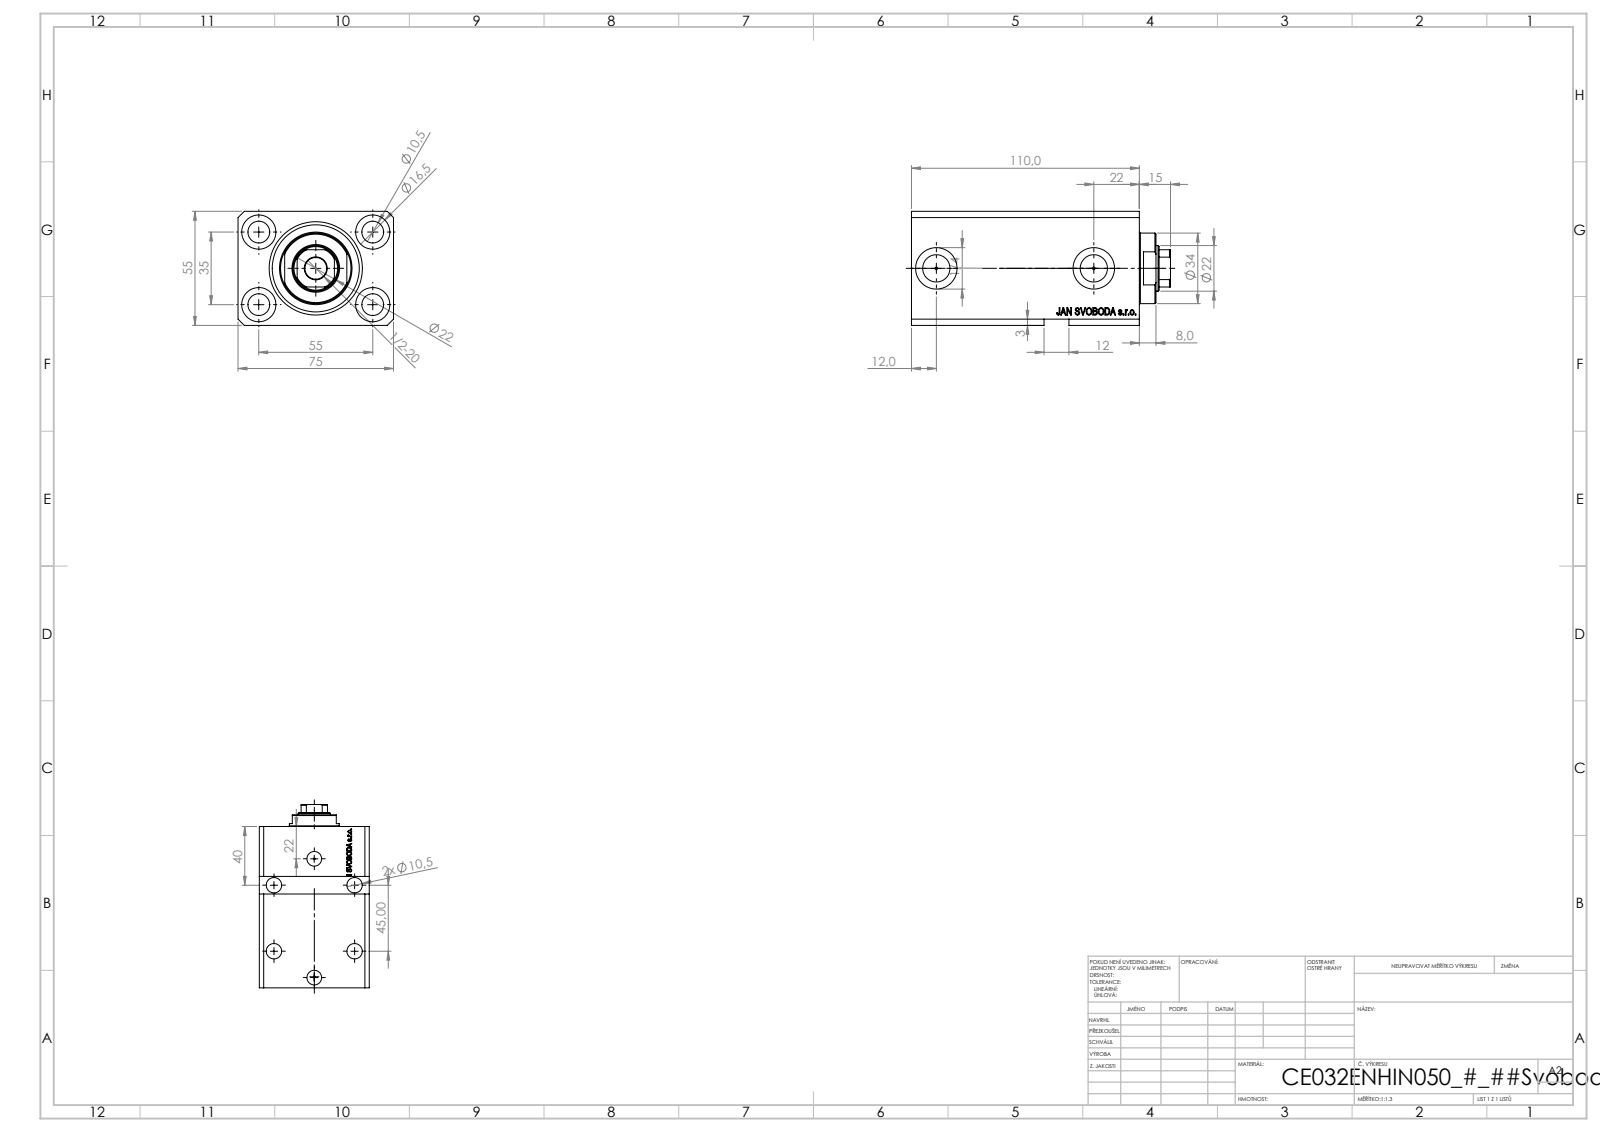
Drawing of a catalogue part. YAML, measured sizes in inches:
part_name: "V250CE_VC_E; V250CE_C_VCP; V250CE_E_Body"
step_written_by: "SolidWorks 2019 (CONFIG_CONTROL_DESIGN)"
units: inches
bodies: {solids: 3, faces: 914, planar: 438, cylindrical: 104, other: 372}
overall_size: [4.921, 2.953, 2.165]
volume: 22.52
surface_area: 132.4
round_holes:
  - {diameter: 0.413, count: 9}
  - {diameter: 0.049, count: 4}
  - {diameter: 0.65, count: 4}
  - {diameter: 0.394, count: 2}
  - {diameter: 0.518, count: 2}
  - {diameter: 0.787, count: 2}
  - {diameter: 0.866, count: 1}
  - {diameter: 1.26, count: 1}
  - {diameter: 1.772, count: 1}
round_bosses_or_shafts:
  - {diameter: 1.339, count: 1}
partial_cylinders:
  - {radius: 0.413, count: 1}
face_to_face_distances: [2.165, 2.953, 0.591, 4.331, 3.74, 0.39, 3.35, 3.941, 0.433, 3.898]
hole_center_spacings: [1.283, 1.294, 2.165, 2.706, 1.283, 1.378, 1.772, 2.567]
